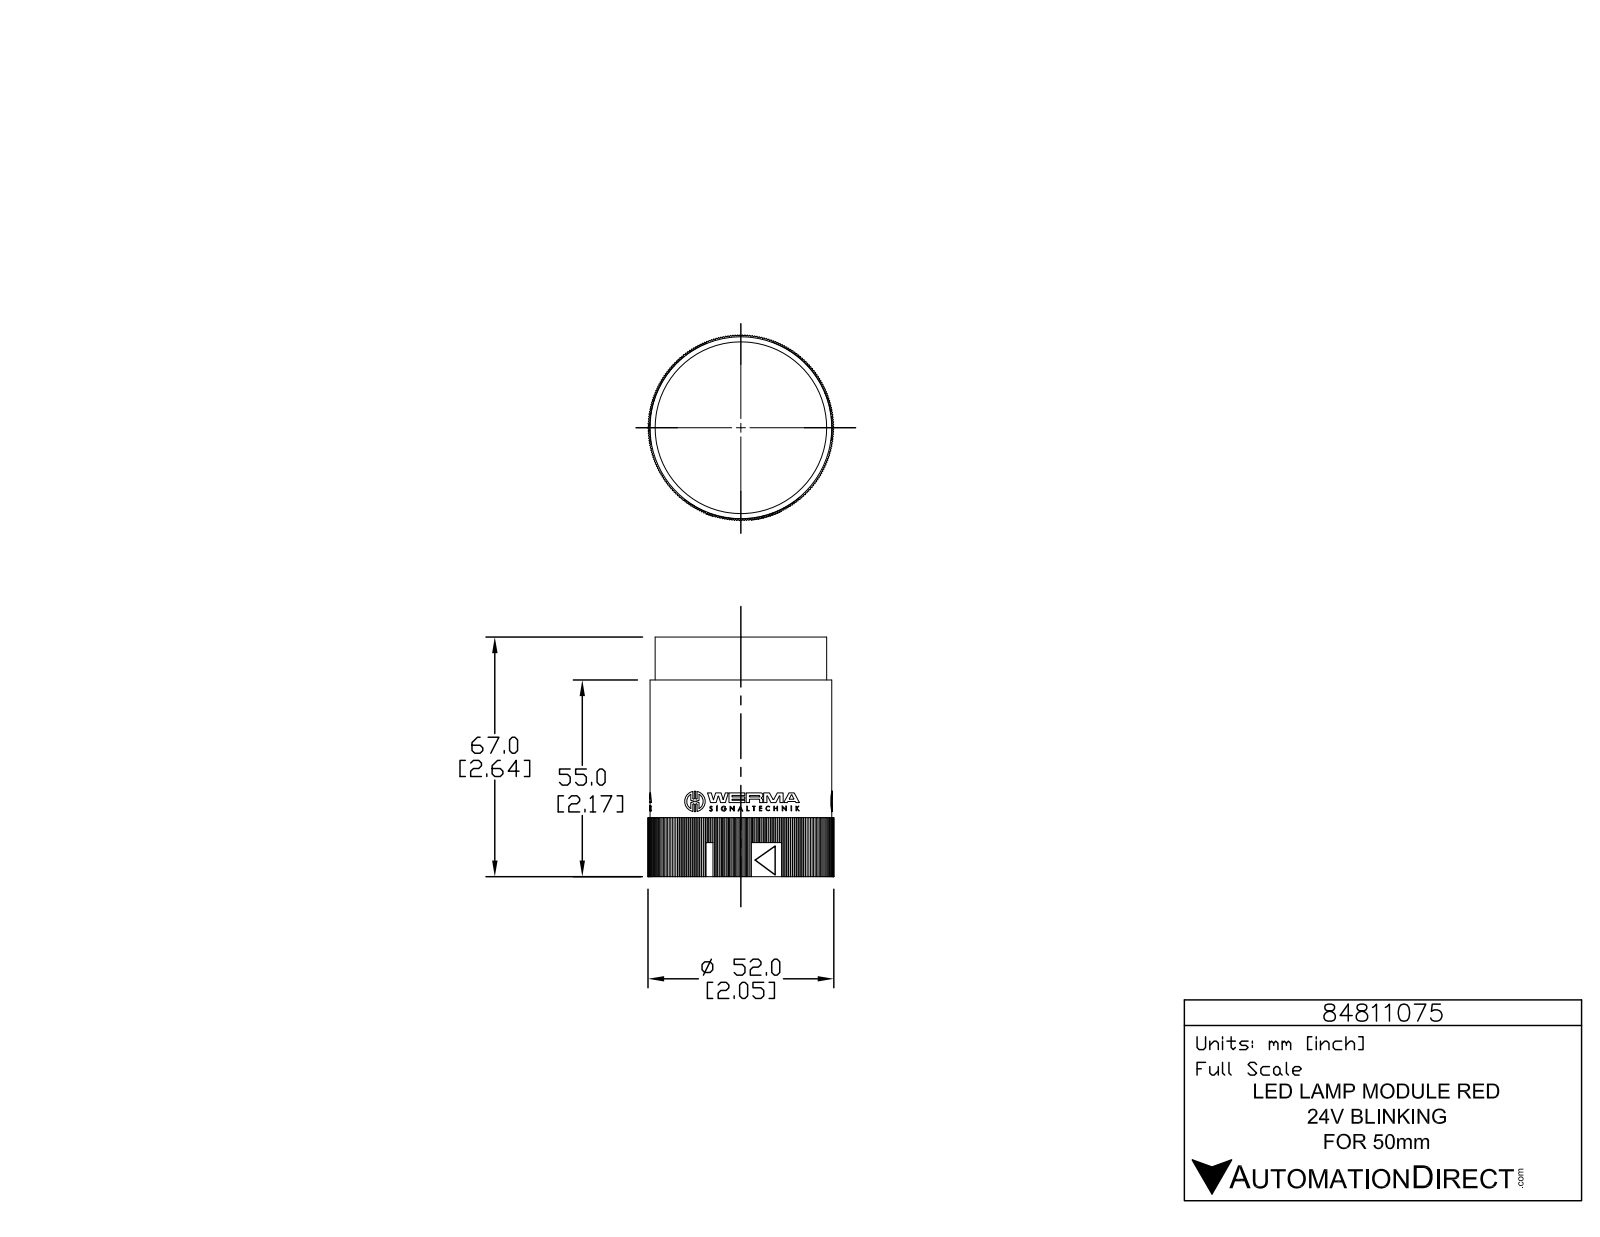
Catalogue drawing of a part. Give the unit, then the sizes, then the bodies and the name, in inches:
Units: inches
Overall size (bounding box): 2.638 × 2.047 × 2.047
Round holes (diameter × count): ⌀0.039 ×3, ⌀1.898 ×1
Round bosses / shafts (diameter × count): ⌀0.226 ×3, ⌀0.056 ×3, ⌀2.002 ×1, ⌀1.89 ×1
Partial cylindrical surfaces — rounded edges, fillets, slot ends (radius × count): R0.008 ×6, R0.008 ×6, R0.008 ×6, R0.131 ×6, R0.004 ×3, R0.005 ×3, R0.008 ×3, R0.008 ×3
Main face-to-face distances: 2.165, 1.428, 1.429, 1.429, 0.472, 2.638, 1.428, 1.428, 1.693, 1.988
Volume: 6.873 in³ · Surface area: 27.62 in²
Bodies: 1 solid, 1265 faces (1020 planar, 245 cylindrical, 0 other)
Part name (STEP PRODUCT): 84811075
STEP written by: SolidWorks 2015 (AUTOMOTIVE_DESIGN)
